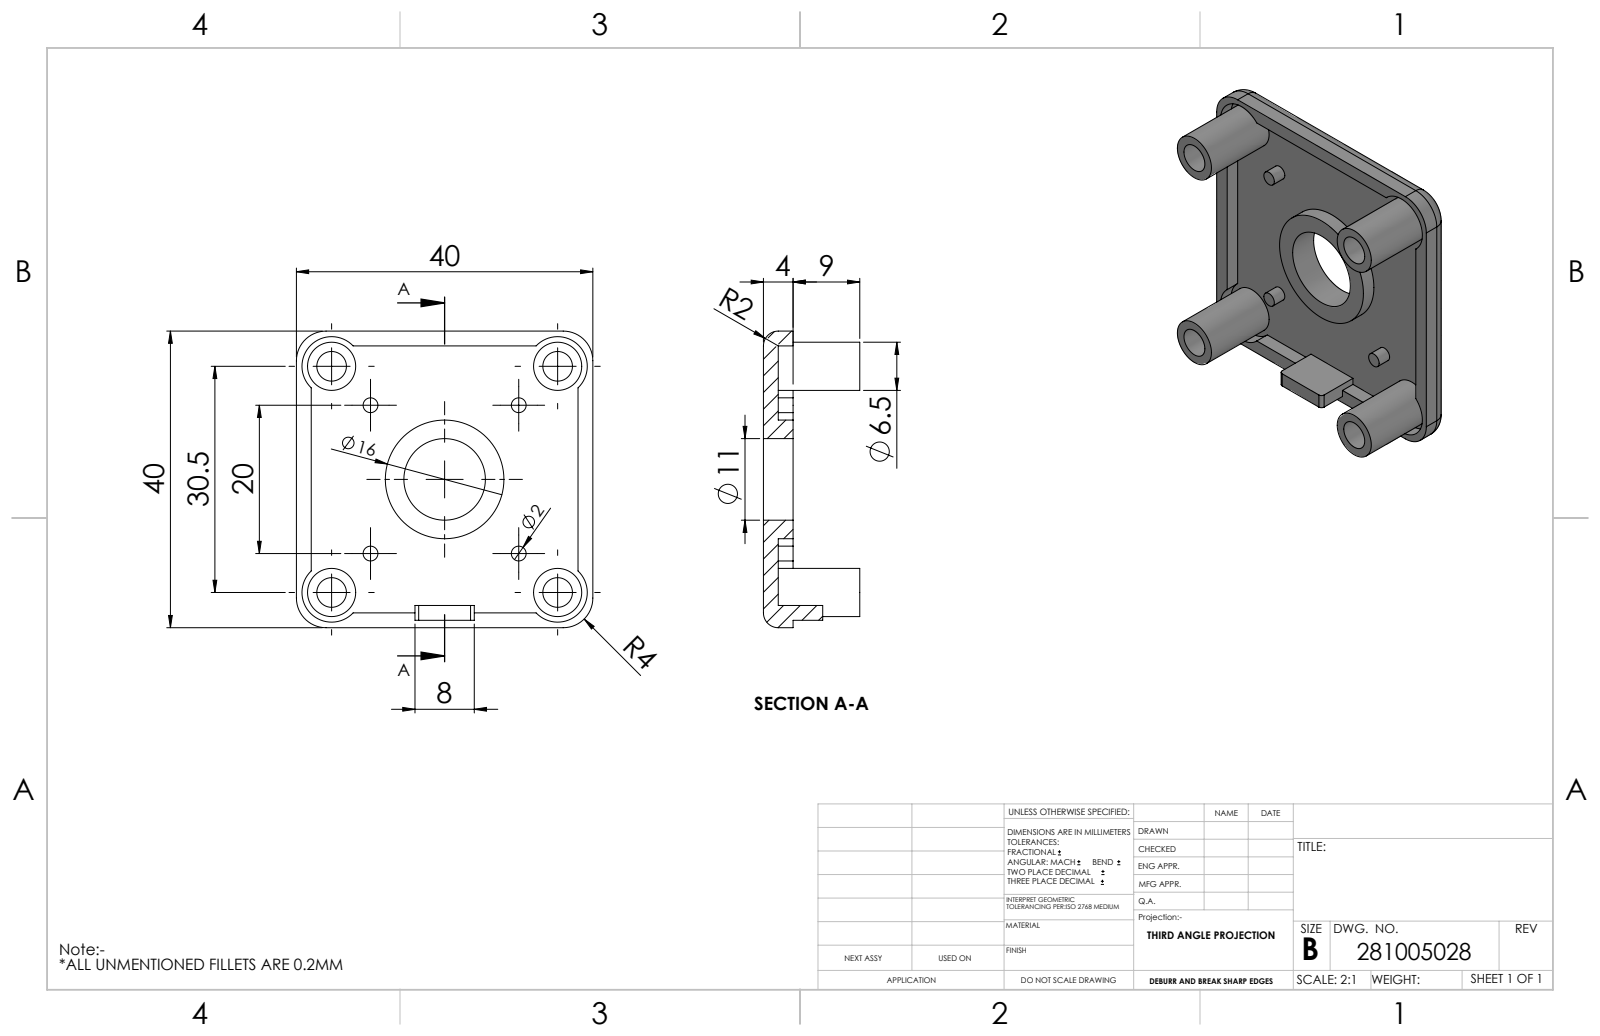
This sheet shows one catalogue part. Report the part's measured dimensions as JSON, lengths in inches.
{"part_name": "281005028 Abdeckkappe 40x40L mit Loch", "step_written_by": "Autodesk Inventor 2019 (AUTOMOTIVE_DESIGN)", "units": "inches", "bodies": {"solids": 1, "faces": 62, "planar": 30, "cylindrical": 28, "other": 4}, "overall_size": [1.575, 1.575, 0.512], "volume_in3": 0.279, "surface_area_in2": 8.657, "round_holes": [[0.157, 4], [0.433, 1]], "round_bosses_or_shafts": [[0.256, 4], [0.079, 4], [0.63, 1]], "partial_cylinders_radius": [[0.157, 8], [0.079, 4], [0.02, 2]], "face_to_face_distances": [0.079, 0.157, 1.496, 1.575, 0.039, 1.417, 0.354, 0.433, 0.512, 1.457], "hole_center_spacings": [0.849, 1.201, 1.698]}
